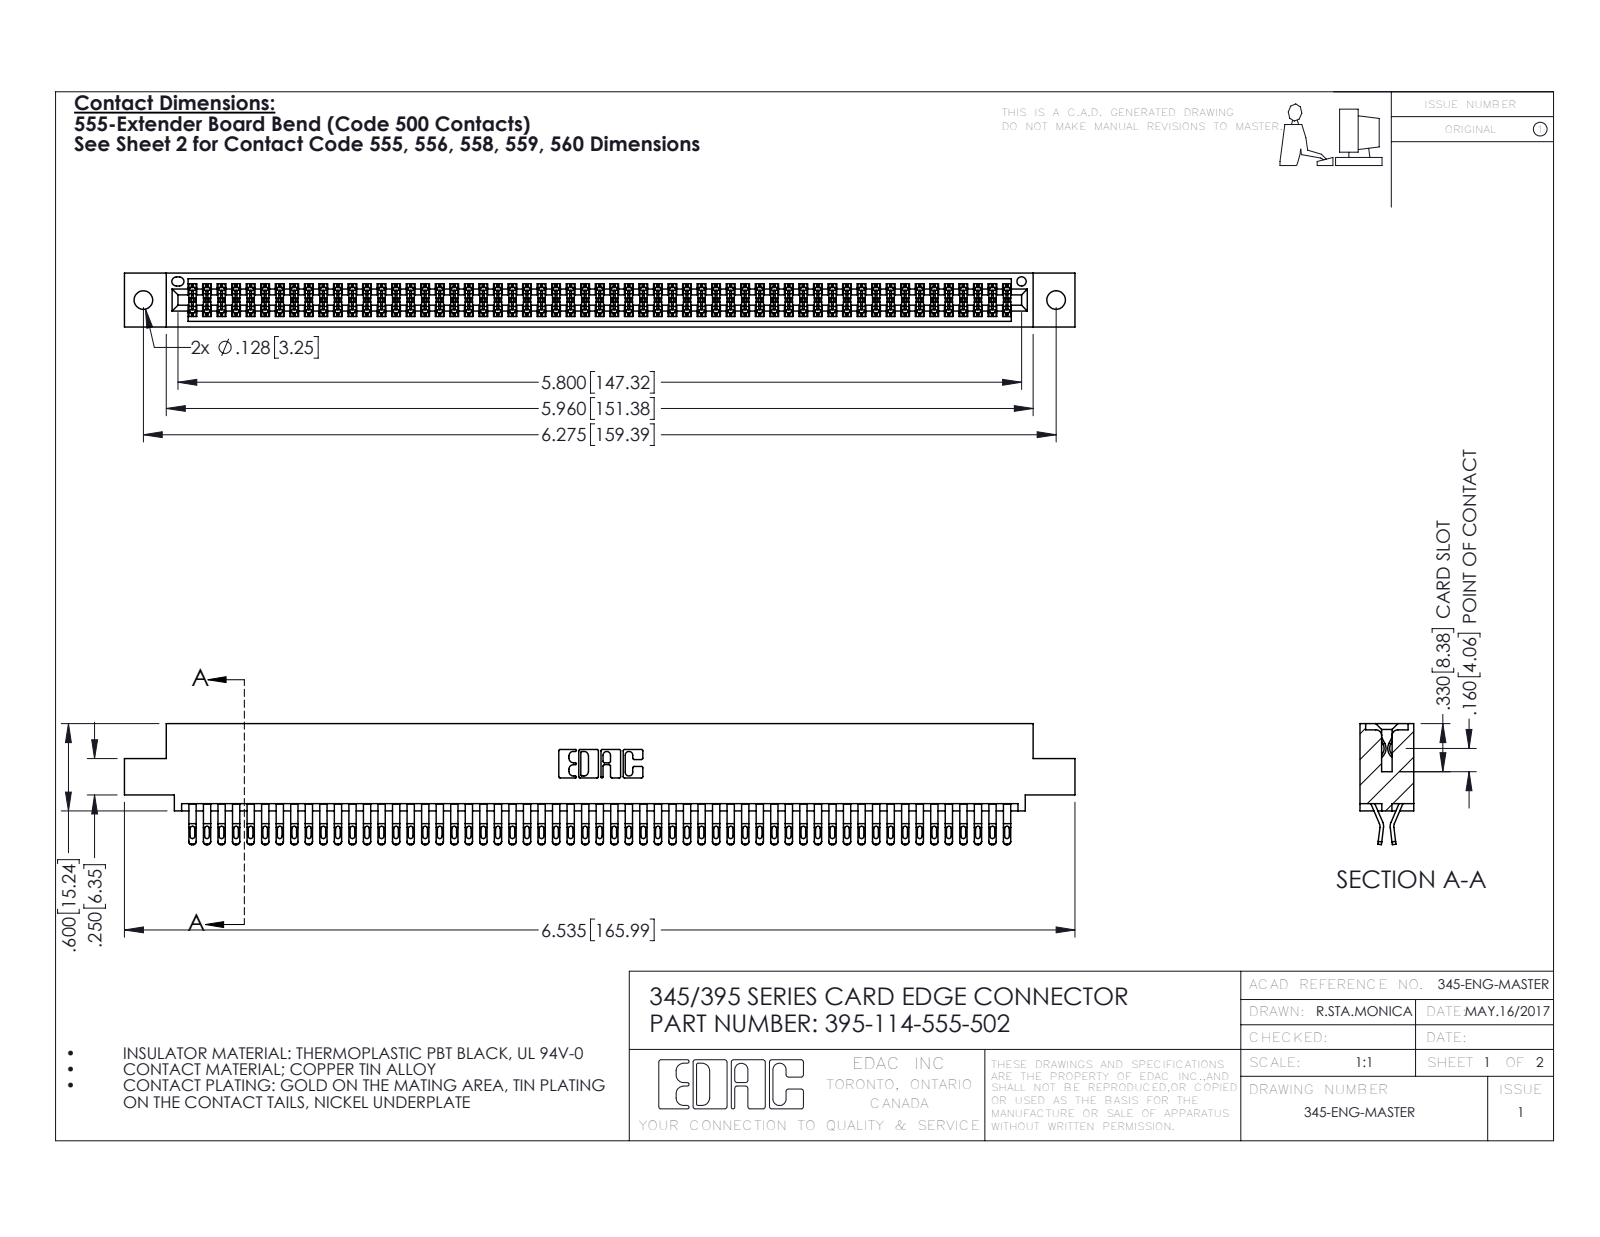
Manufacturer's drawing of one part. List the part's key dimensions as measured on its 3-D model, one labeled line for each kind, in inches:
Part name (STEP PRODUCT): 345-292-001_555 Tail; 345 Part_0.110 Offset - 0.128 Dia; 395-114-555-502
STEP written by: SolidWorks 2016 (CONFIG_CONTROL_DESIGN)
Units: inches
Bodies: 115 solids, 6514 faces (3618 planar, 2896 cylindrical, 0 other)
Overall size (bounding box): 6.535 × 0.832 × 0.37
Volume: 1.006 in³ · Surface area: 39.72 in²
Round holes (diameter × count): ⌀0.128 ×2, ⌀0.064 ×1
Partial cylindrical surfaces — rounded edges, fillets, slot ends (radius × count): R0.016 ×285, R0.02 ×228, R0.006 ×171, R0.01 ×22, R0.007 ×6, R0.031 ×6, R0.026 ×3, R0.01 ×2
Main face-to-face distances: 0.298, 0.072, 0.025, 0.37, 0.2, 0.098, 0.272, 0.225, 0.175, 0.149
Hole centre spacings: 0.27, 6.039, 6.275
